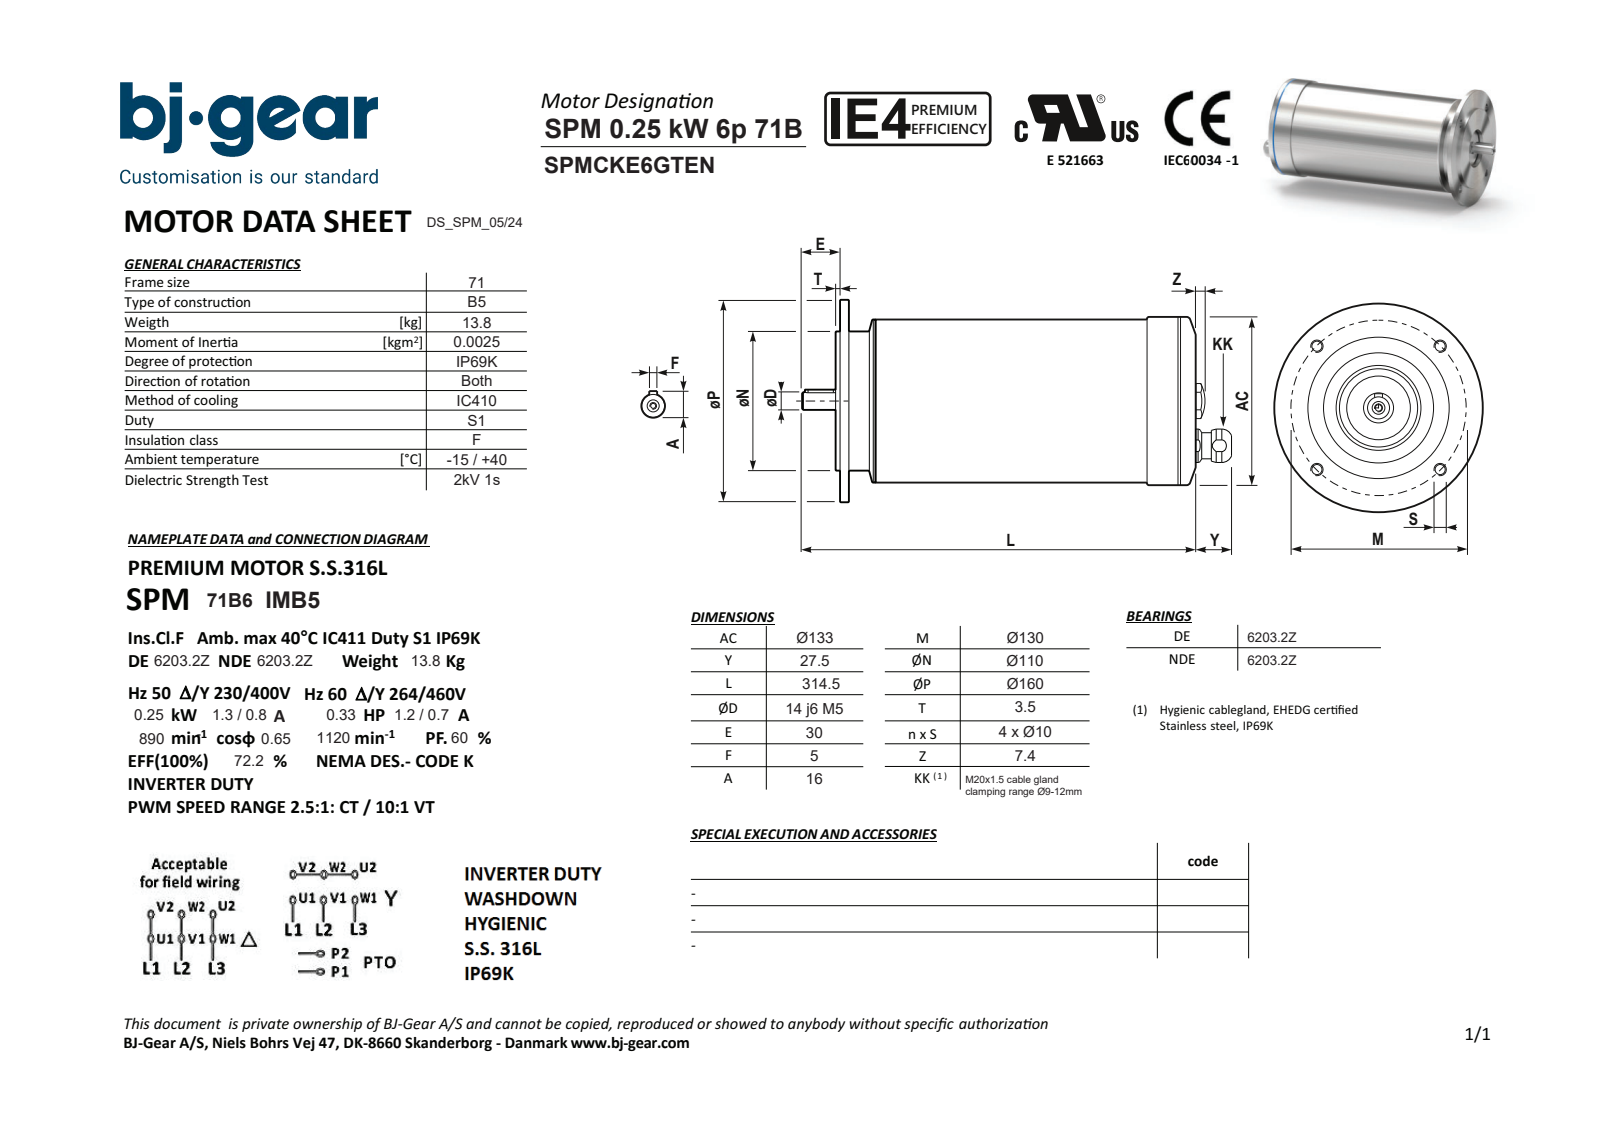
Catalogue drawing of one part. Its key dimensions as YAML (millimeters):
part_name: "SPMCKE6GTENN4KSA1-N---NNN"
step_written_by: "Solid Edge (AUTOMOTIVE_DESIGN)"
units: millimeters
bodies: {solids: 1, faces: 86, planar: 31, cylindrical: 30, other: 25}
overall_size: [342, 160, 160]
volume: 3756000
surface_area: 167604
round_holes:
  - {diameter: 10, count: 4}
  - {diameter: 4.13, count: 1}
  - {diameter: 5.3, count: 1}
  - {diameter: 7, count: 1}
  - {diameter: 13.4, count: 1}
  - {diameter: 52, count: 1}
round_bosses_or_shafts:
  - {diameter: 160, count: 1}
  - {diameter: 133, count: 1}
  - {diameter: 132.98, count: 1}
  - {diameter: 129, count: 1}
  - {diameter: 128.98, count: 1}
  - {diameter: 110, count: 1}
  - {diameter: 20, count: 1}
  - {diameter: 17, count: 1}
partial_cylinders:
  - {radius: 2.5, count: 2}
  - {radius: 12.8, count: 1}
face_to_face_distances: [7, 277.5, 284.5, 288, 10.5, 3.5, 279, 1.5, 5.5, 9]
hole_center_spacings: [65, 91.92, 47.49, 92.23, 129.99, 34]
